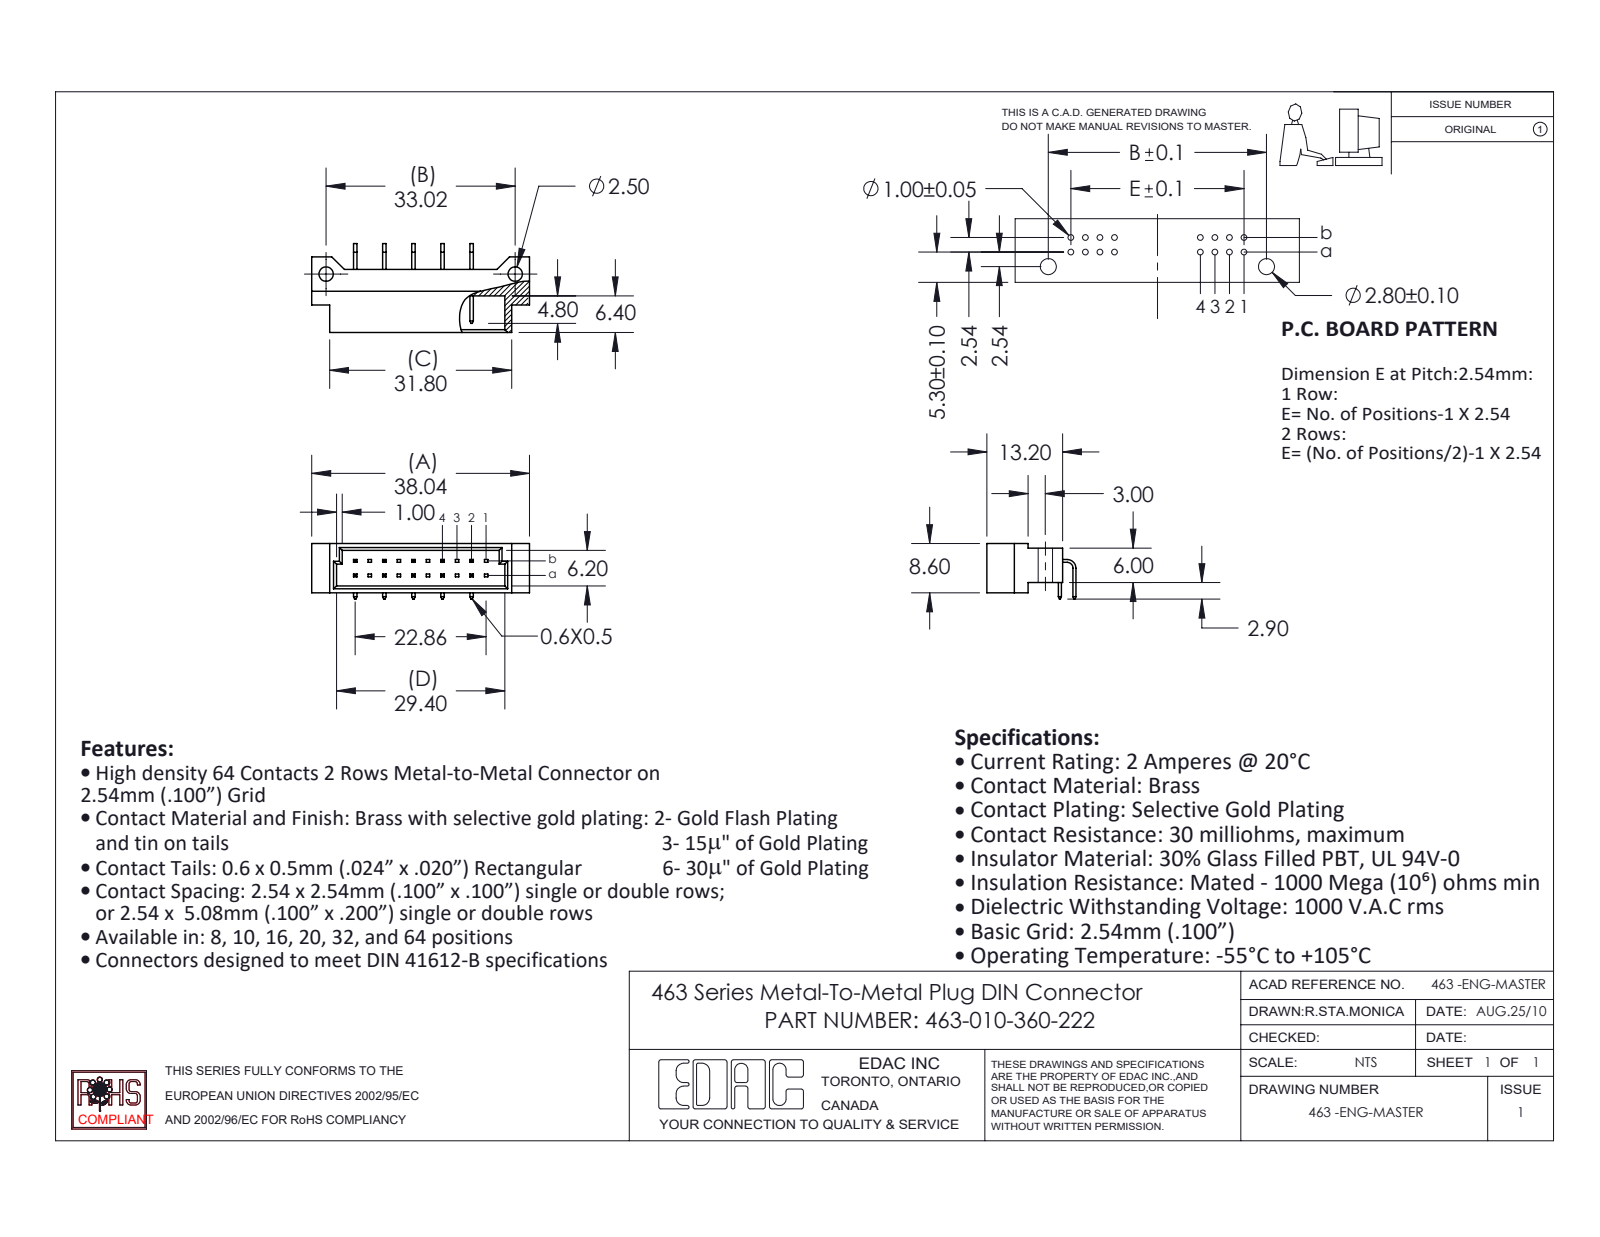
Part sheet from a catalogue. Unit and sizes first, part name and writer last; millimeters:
Units: millimetres
Overall size (bounding box): 38.04 × 15.53 × 9.7
Round holes (diameter × count): ⌀2.5 ×2
Partial cylindrical surfaces — rounded edges, fillets, slot ends (radius × count): R1.02 ×2, R1.52 ×2
Main face-to-face distances: 1.2, 7.4, 0.6, 0.8, 8.6, 6.2, 6, 6.8, 5.08, 5.6
Hole centre spacings: 33.02
Volume: 1 906 mm³ · Surface area: 2 754 mm²
Bodies: 11 solids, 299 faces (275 planar, 24 cylindrical, 0 other)
Part name (STEP PRODUCT): 463-290-1; 463-290-2; 463-010-360-222; 463 Part_20
STEP written by: SolidWorks 2020 (CONFIG_CONTROL_DESIGN)
